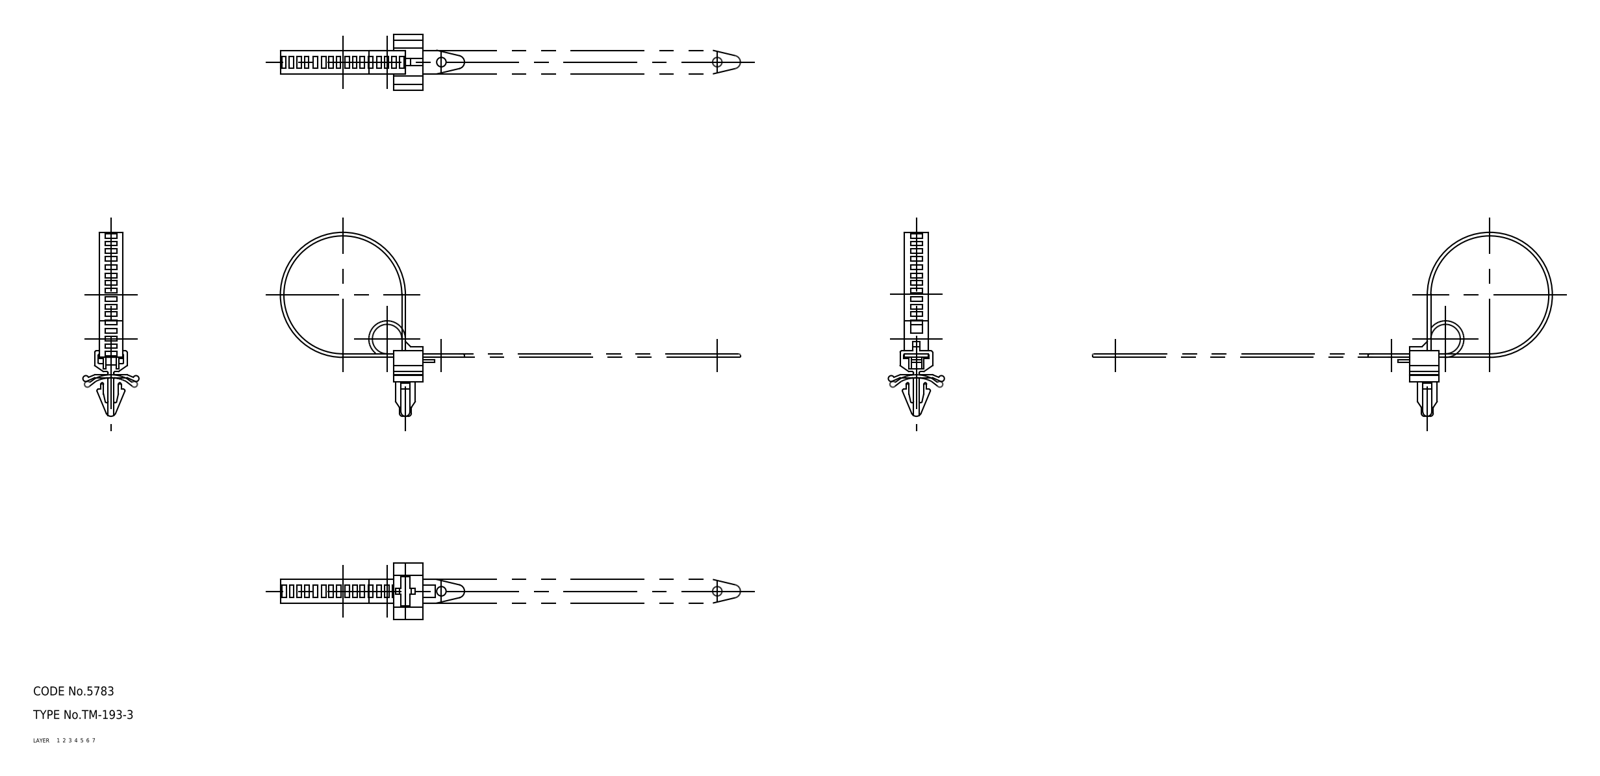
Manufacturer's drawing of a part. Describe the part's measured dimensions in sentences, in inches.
The part is named "clip". Its 3-D file was written by "CADfix (AUTOMOTIVE_DESIGN)". It is 1 solid with 200 faces: 0 planar, 0 cylindrical and 200 other. Overall it measures 2.457 by 2.457 by 0.748 inches. Its volume is 0.143 cubic inches and its surface area 6.715 square inches.
